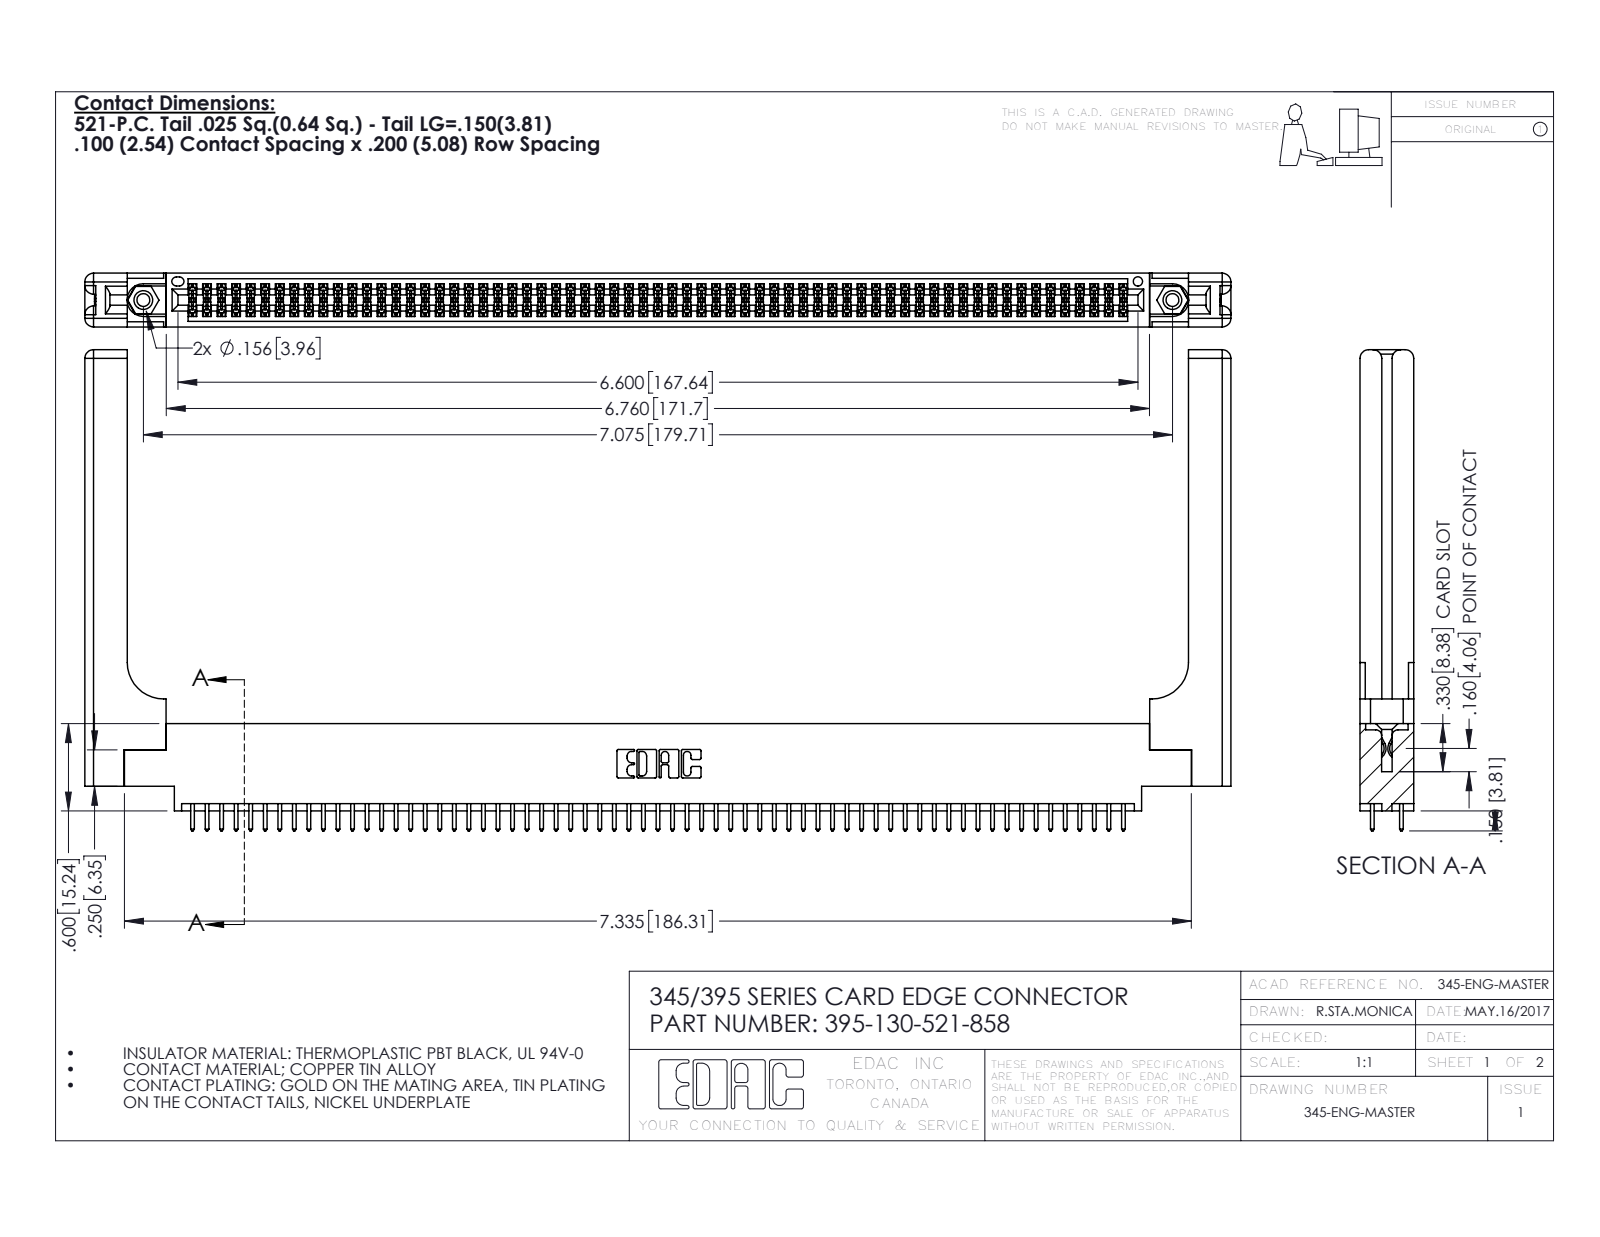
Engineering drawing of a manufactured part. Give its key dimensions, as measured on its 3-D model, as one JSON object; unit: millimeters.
{"part_name": "345-292-001_345-293-121; 345 Part_0.170 Offset - 0.156 Dia-TH; 345-250-001_345-250-001-102; 395-130-521-858 (+1 more)", "step_written_by": "SolidWorks 2016 (CONFIG_CONTROL_DESIGN)", "units": "millimeters", "bodies": {"solids": 135, "faces": 6886, "planar": 4522, "cylindrical": 2304, "other": 60}, "overall_size": [200.1, 84, 9.4], "volume_mm3": 27960, "surface_area_mm2": 34110, "round_holes": [[2.3, 2], [3.2, 2], [4, 2], [1.6, 1]], "round_bosses_or_shafts": [[3.9, 2]], "partial_cylinders_radius": [[0.2, 195], [0.3, 130], [0.3, 22], [1.5, 16], [0.2, 6], [0.8, 6], [0.7, 3], [0.4, 2]], "face_to_face_distances": [1.8, 7.6, 9.4, 2.5, 6.9, 0.6, 5.1, 5.7, 4.4, 3.8], "hole_center_spacings": [6.9, 173.7, 179.7]}
